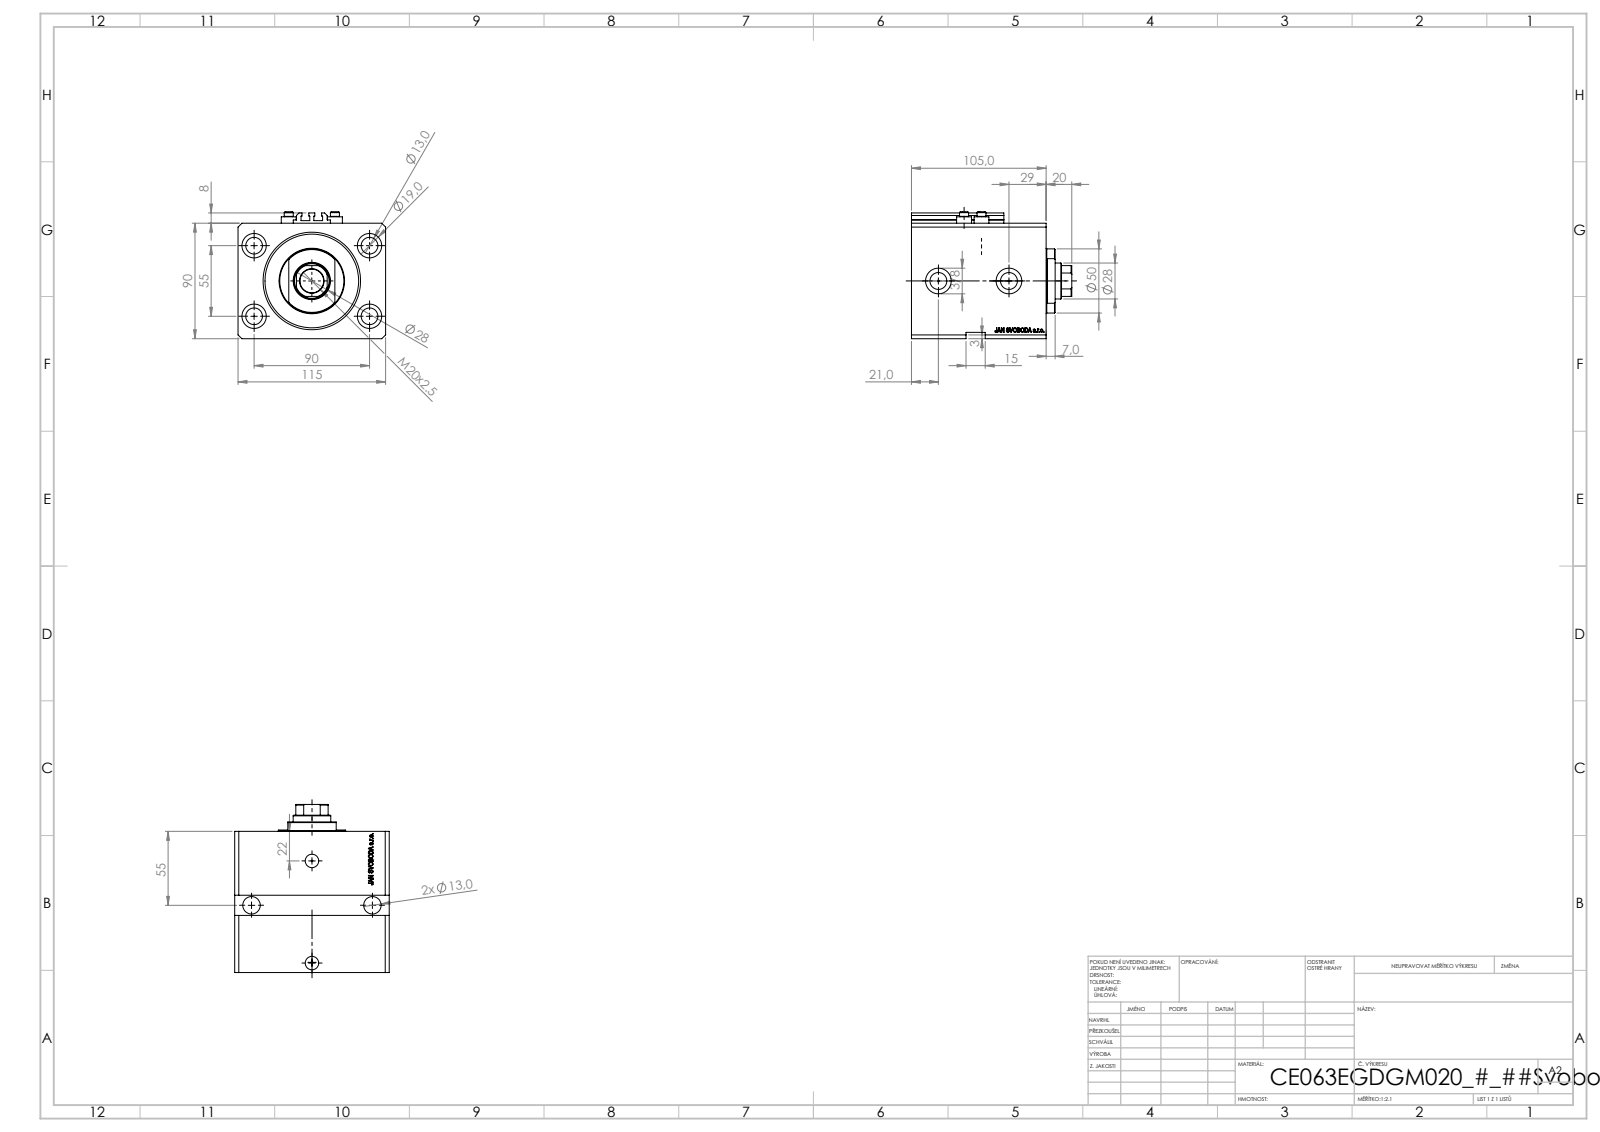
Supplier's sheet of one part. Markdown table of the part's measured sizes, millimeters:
| quantity | value |
| --- | --- |
| part name | ALLEN BOLT V250CE; V250CE_C_VCP; V250CE_E_Body; V250CE_VC_E |
| STEP written by | SolidWorks 2019 (CONFIG_CONTROL_DESIGN) |
| units | millimeters |
| bodies | 8 solids, 1123 faces (547 planar, 138 cylindrical, 438 other) |
| overall size | 125 × 115 × 99 |
| volume | 950 937 mm³ |
| surface area | 155 133 mm² |
| round holes (diameter × count) | 13 × 6, 1.25 × 4, 4 × 4, 19 × 4, 10 × 2, 13.16 × 2, 20 × 2, 18.5 × 1, 28 × 1, 63 × 1, 76 × 1 |
| round bosses / shafts (diameter × count) | 11.6 × 4, 7 × 4, 50 × 1 |
| partial cylindrical surfaces (radius × count) | 0.2 × 10, 13.5 × 1 |
| main face-to-face distances | 90, 20, 115, 85, 105, 87.1, 17.9, 67.1, 40, 65 |
| hole center spacings | 52.74, 55, 90, 13.6, 27.39, 28.46, 33.62, 36 |
